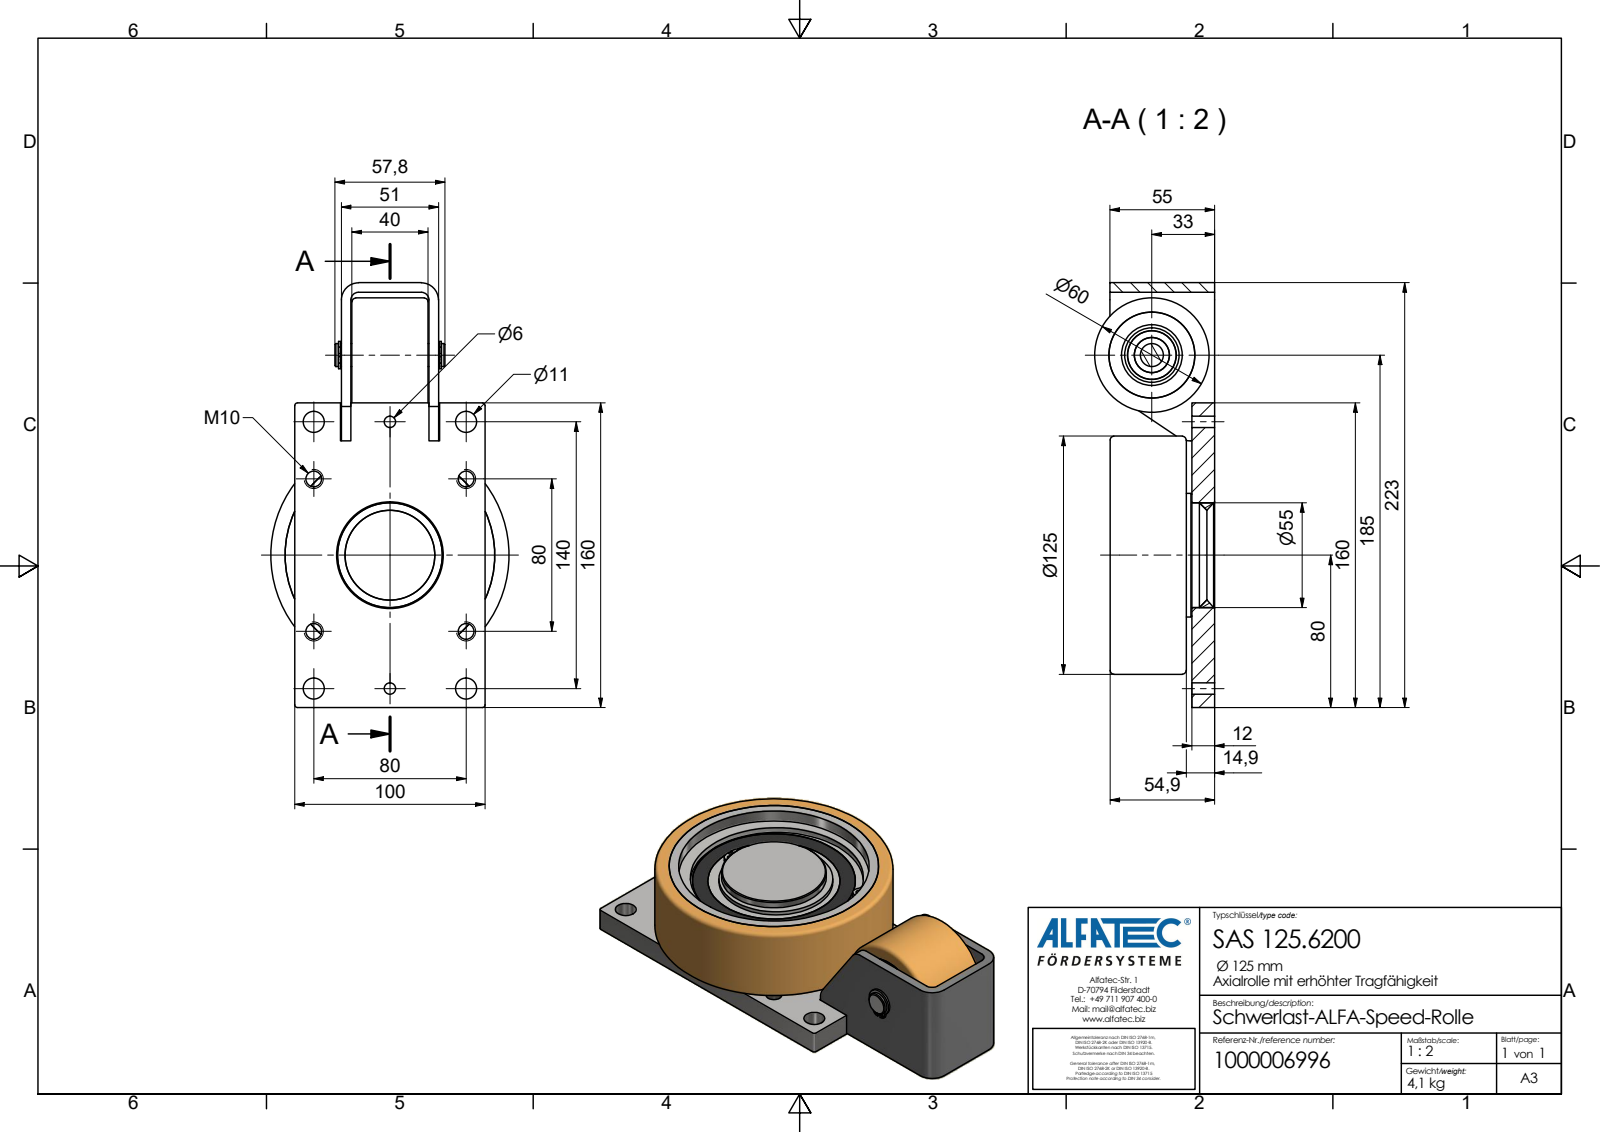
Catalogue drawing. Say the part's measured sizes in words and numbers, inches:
The part is named "SAS 125.6200_Kontur". Its 3-D file was written by "Autodesk Inventor 2020 (AP242_MANAGED_MODEL_BASED_3D_ENGINEERING_MIM_LF)". It is 1 solid with 113 faces: 57 planar, 45 cylindrical and 11 other. Overall it measures 8.78 by 4.921 by 2.48 inches. Its volume is 51.6 cubic inches and its surface area 167.6 square inches. Round holes: 4 of diameter 0.33, 4 of diameter 0.433, 2 of diameter 0.067, 2 of diameter 0.236, 1 of diameter 1.26. Round bosses or shafts: 1 of diameter 4.921, 1 of diameter 2.559, 1 of diameter 2.362, 1 of diameter 0.567, 1 of diameter 0.472, 1 of diameter 0.453. Partial cylindrical surfaces (rounded edges, fillets, slot ends): 4 of radius 0.059, 2 of radius 0.1, 2 of radius 0.157, 2 of radius 0.354, 1 of radius 0.236, 1 of radius 0.472. The main face-to-face distances are 0.472, 2.161, 1.689, 1.575, 0.114, 0.197, 0.587, 1.811, 0.02, 0.217. The hole center spacings are 3.15, 1.181, 1.575, 1.969, 3.364, 4.331, 4.608, 5.355.
